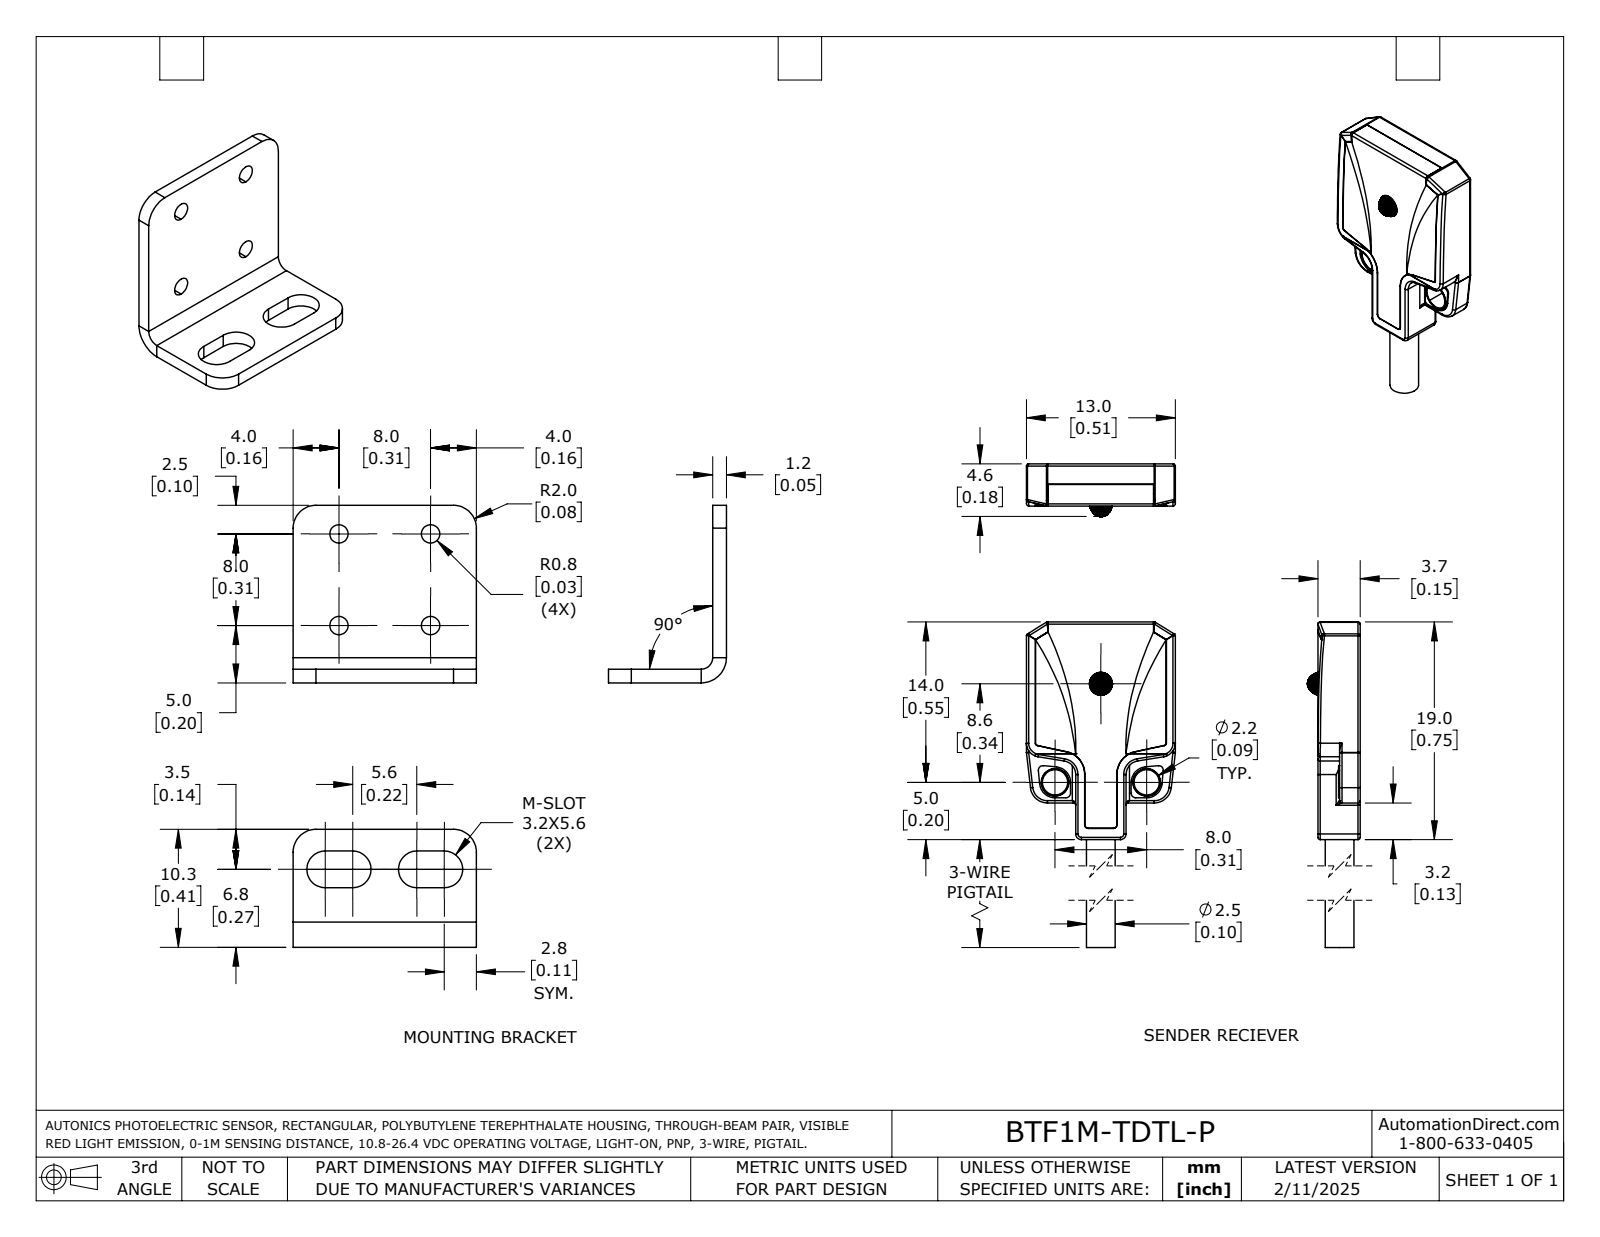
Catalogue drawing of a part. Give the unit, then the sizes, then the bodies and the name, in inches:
Units: inches
Overall size (bounding box): 3.102 × 1.004 × 0.61
Round holes (diameter × count): ⌀0.063 ×4, ⌀0.087 ×2, ⌀0.094 ×2, ⌀0.098 ×2
Round bosses / shafts (diameter × count): ⌀0.142 ×2, ⌀0.138 ×2, ⌀0.093 ×2, ⌀0.079 ×2
Partial cylindrical surfaces — rounded edges, fillets, slot ends (radius × count): R0.008 ×60, R0.063 ×8, R0.079 ×8, R0.012 ×6, R0.016 ×4, R0.039 ×4, R0.047 ×4, R0.009 ×2
Main face-to-face distances: 0.047, 2.339, 2.291, 0.146, 2.193, 2.146, 2.386, 0.193, 0.098, 2
Hole centre spacings: 0.315, 0.445, 2.15
Volume: 0.148 in³ · Surface area: 5.41 in²
Bodies: 12 solids, 1218 faces (332 planar, 266 cylindrical, 620 other)
Part name (STEP PRODUCT): BTF1M-TDTL_BTF1M-TDTL-P_BTF1M-TDTD_BTF1M-TDTD-P; EMITTER; RECIEVER
STEP written by: SolidWorks 2024 (AUTOMOTIVE_DESIGN)
